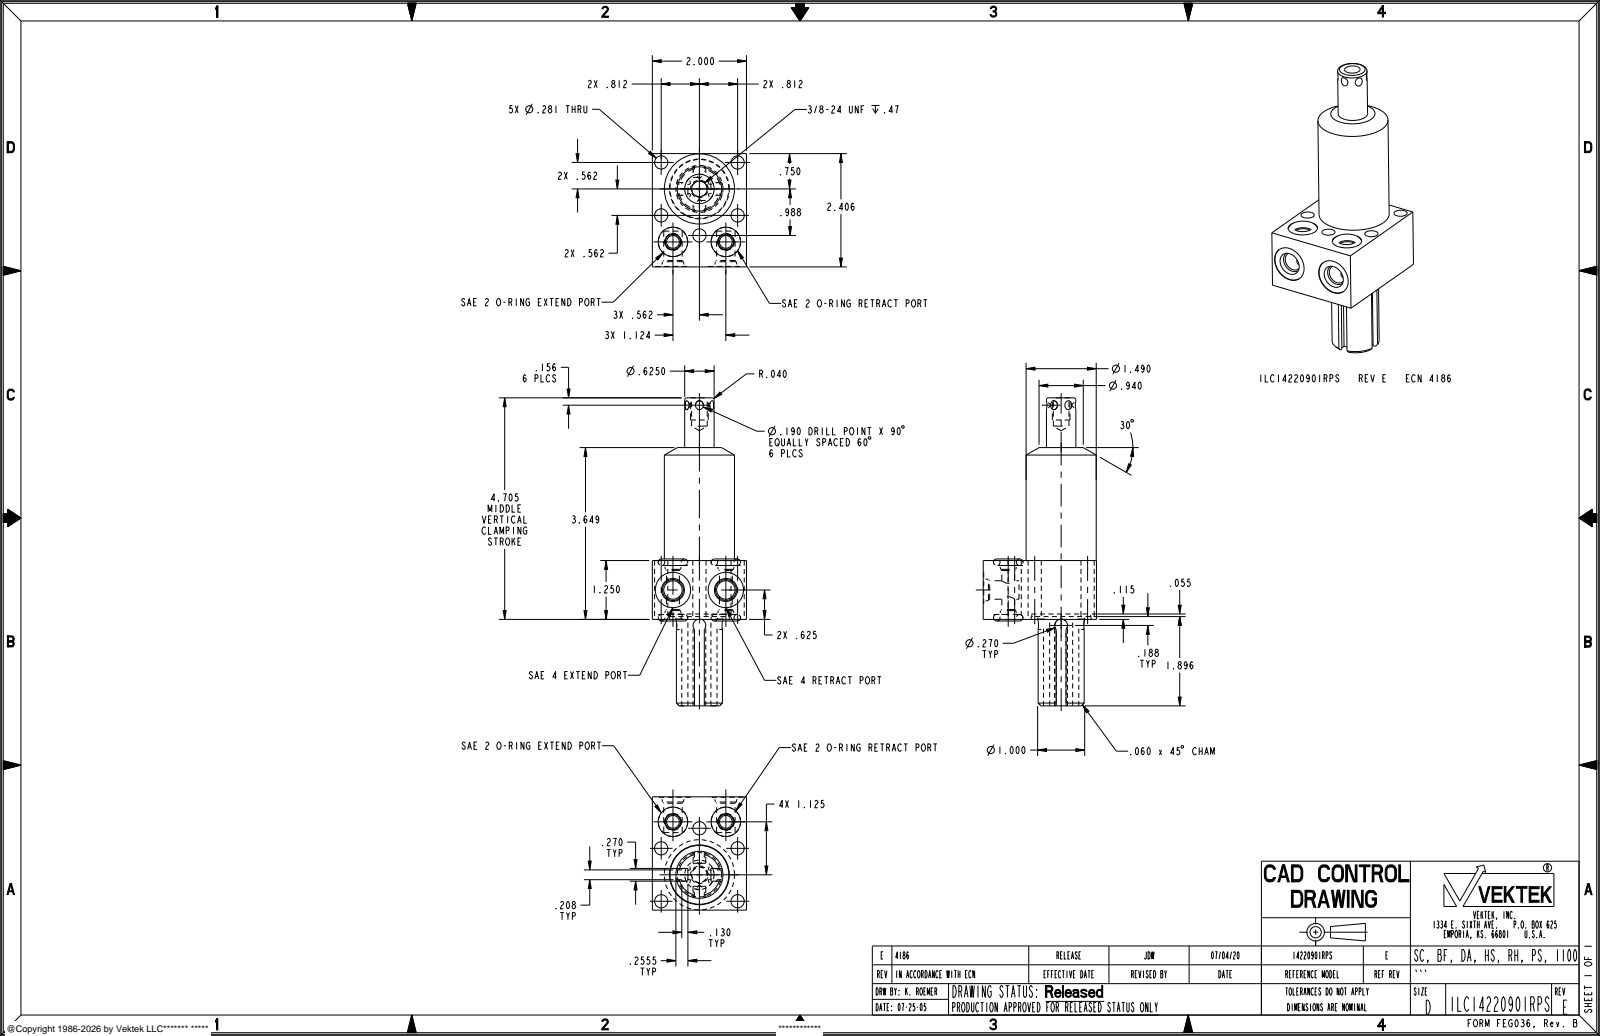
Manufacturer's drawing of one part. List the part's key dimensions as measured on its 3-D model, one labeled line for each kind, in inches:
Part name (STEP PRODUCT): ILC14220901RPS
STEP written by: PRO/ENGINEER BY PARAMETRIC TECHNOLOGY CORPORATION, 2013320 (AUTOMOTIVE_DESIGN)
Units: inches
Bodies: 5 solids, 162 faces (48 planar, 52 cylindrical, 62 other)
Overall size (bounding box): 6.541 × 2.406 × 2
Volume: 10.62 in³ · Surface area: 56.37 in²
Round holes (diameter × count): ⌀0.281 ×5, ⌀0.272 ×2, ⌀0.392 ×2, ⌀0.625 ×2, ⌀0.75 ×2, ⌀0.332 ×1, ⌀1.27 ×1
Round bosses / shafts (diameter × count): ⌀1.49 ×1, ⌀1.25 ×1, ⌀1 ×1, ⌀0.625 ×1, ⌀0.375 ×1
Partial cylindrical surfaces — rounded edges, fillets, slot ends (radius × count): R0.135 ×2
Main face-to-face distances: 2, 1.25, 0.109, 0.38, 2.406, 0.141, 0.348, 0.031, 0.239, 0.756
Hole centre spacings: 0.987, 1.124, 0.578, 0.616, 0.917, 1.257, 1.485, 1.624
